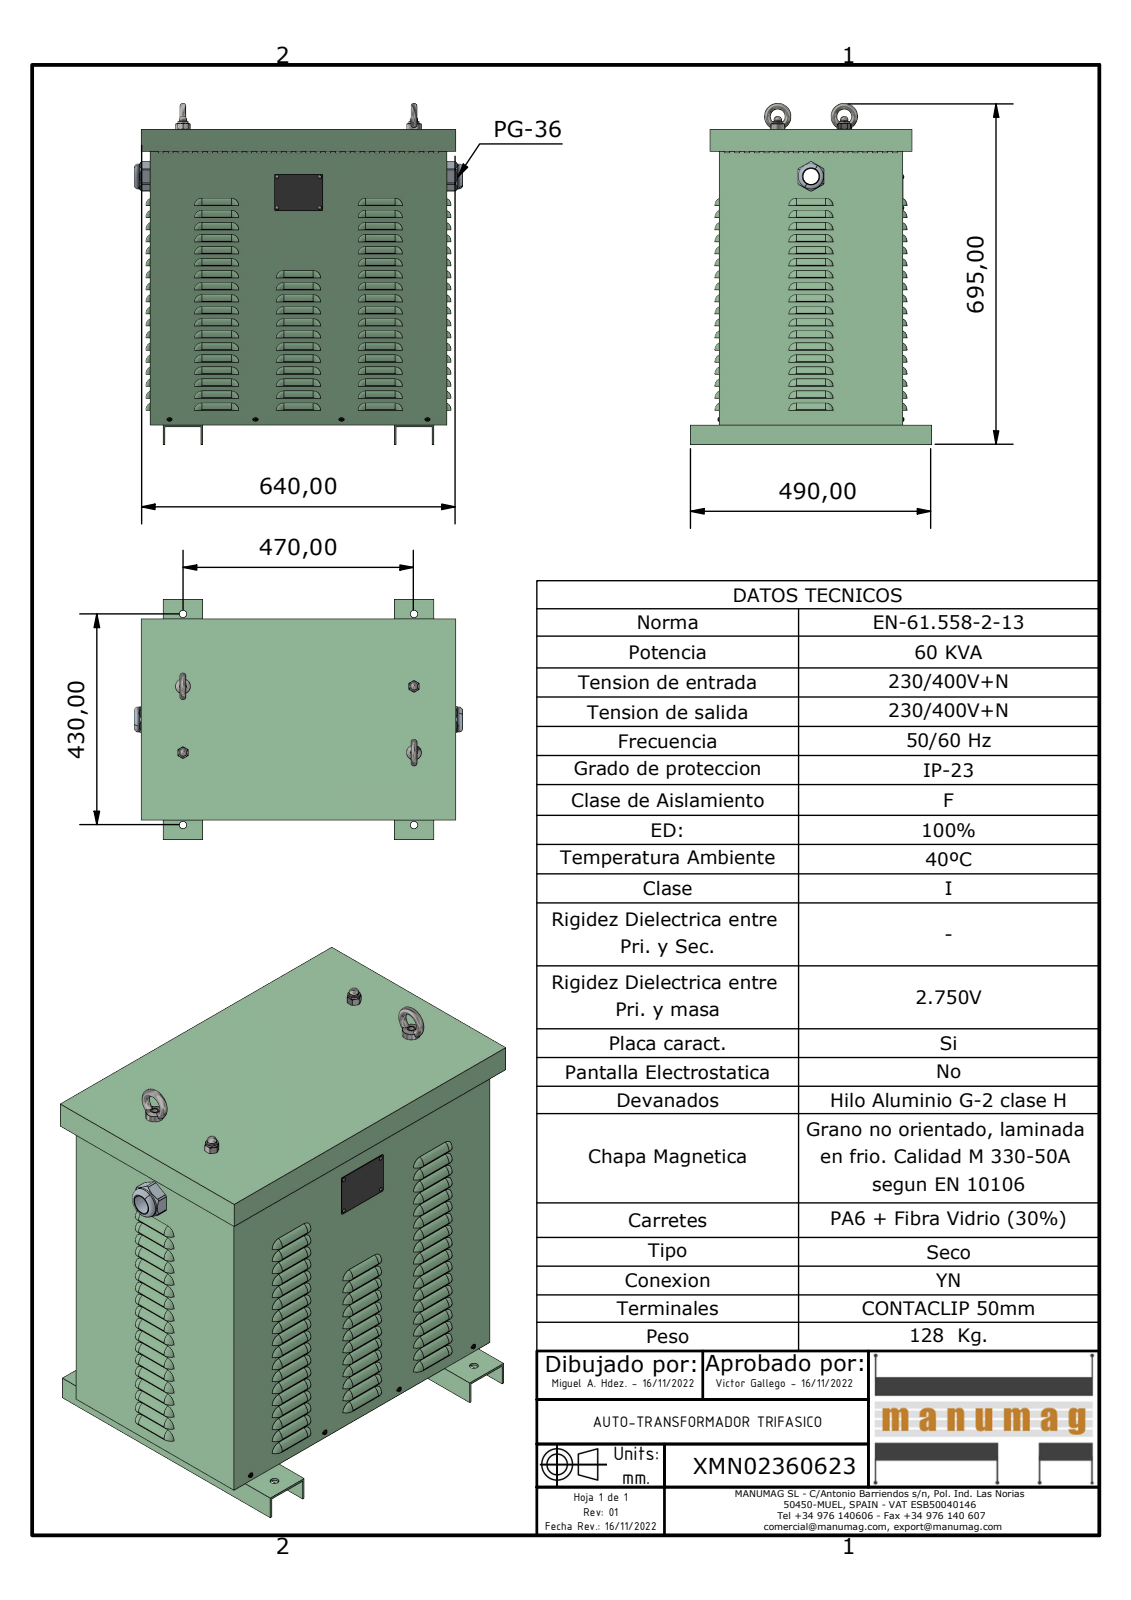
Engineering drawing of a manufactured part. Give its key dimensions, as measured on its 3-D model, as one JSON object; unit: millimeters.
{"part_name": "XMN02360623; JE060 - JE075 CUERPO; JE060 - JE075 BASE; JE060 TAPA SUPERIOR (+7 more)", "step_written_by": "Autodesk Inventor 2023 (AUTOMOTIVE_DESIGN)", "units": "millimeters", "bodies": {"solids": 24, "faces": 2907, "planar": 1145, "cylindrical": 1024, "other": 738}, "overall_size": [695, 668.2, 490], "volume_mm3": 4615000, "surface_area_mm2": 4047000, "round_holes": [[11, 364], [15, 8], [4, 4], [5, 4], [10.11, 2], [11.84, 2], [32, 1], [48, 1]], "round_bosses_or_shafts": [[4, 4], [3.62, 4], [3.2, 4], [51.1, 2], [30, 2], [21, 2], [15.6, 2], [47.45, 1]], "partial_cylinders_radius": [[14, 132], [7, 72], [15, 72], [3.88, 12], [2.5, 8], [7.5, 8], [2, 4], [30, 2]], "face_to_face_distances": [2, 370, 600, 601, 368, 372, 602, 599, 598, 603], "hole_center_spacings": [30, 21.21, 132, 128.88, 147, 173.76, 279, 469.24]}
